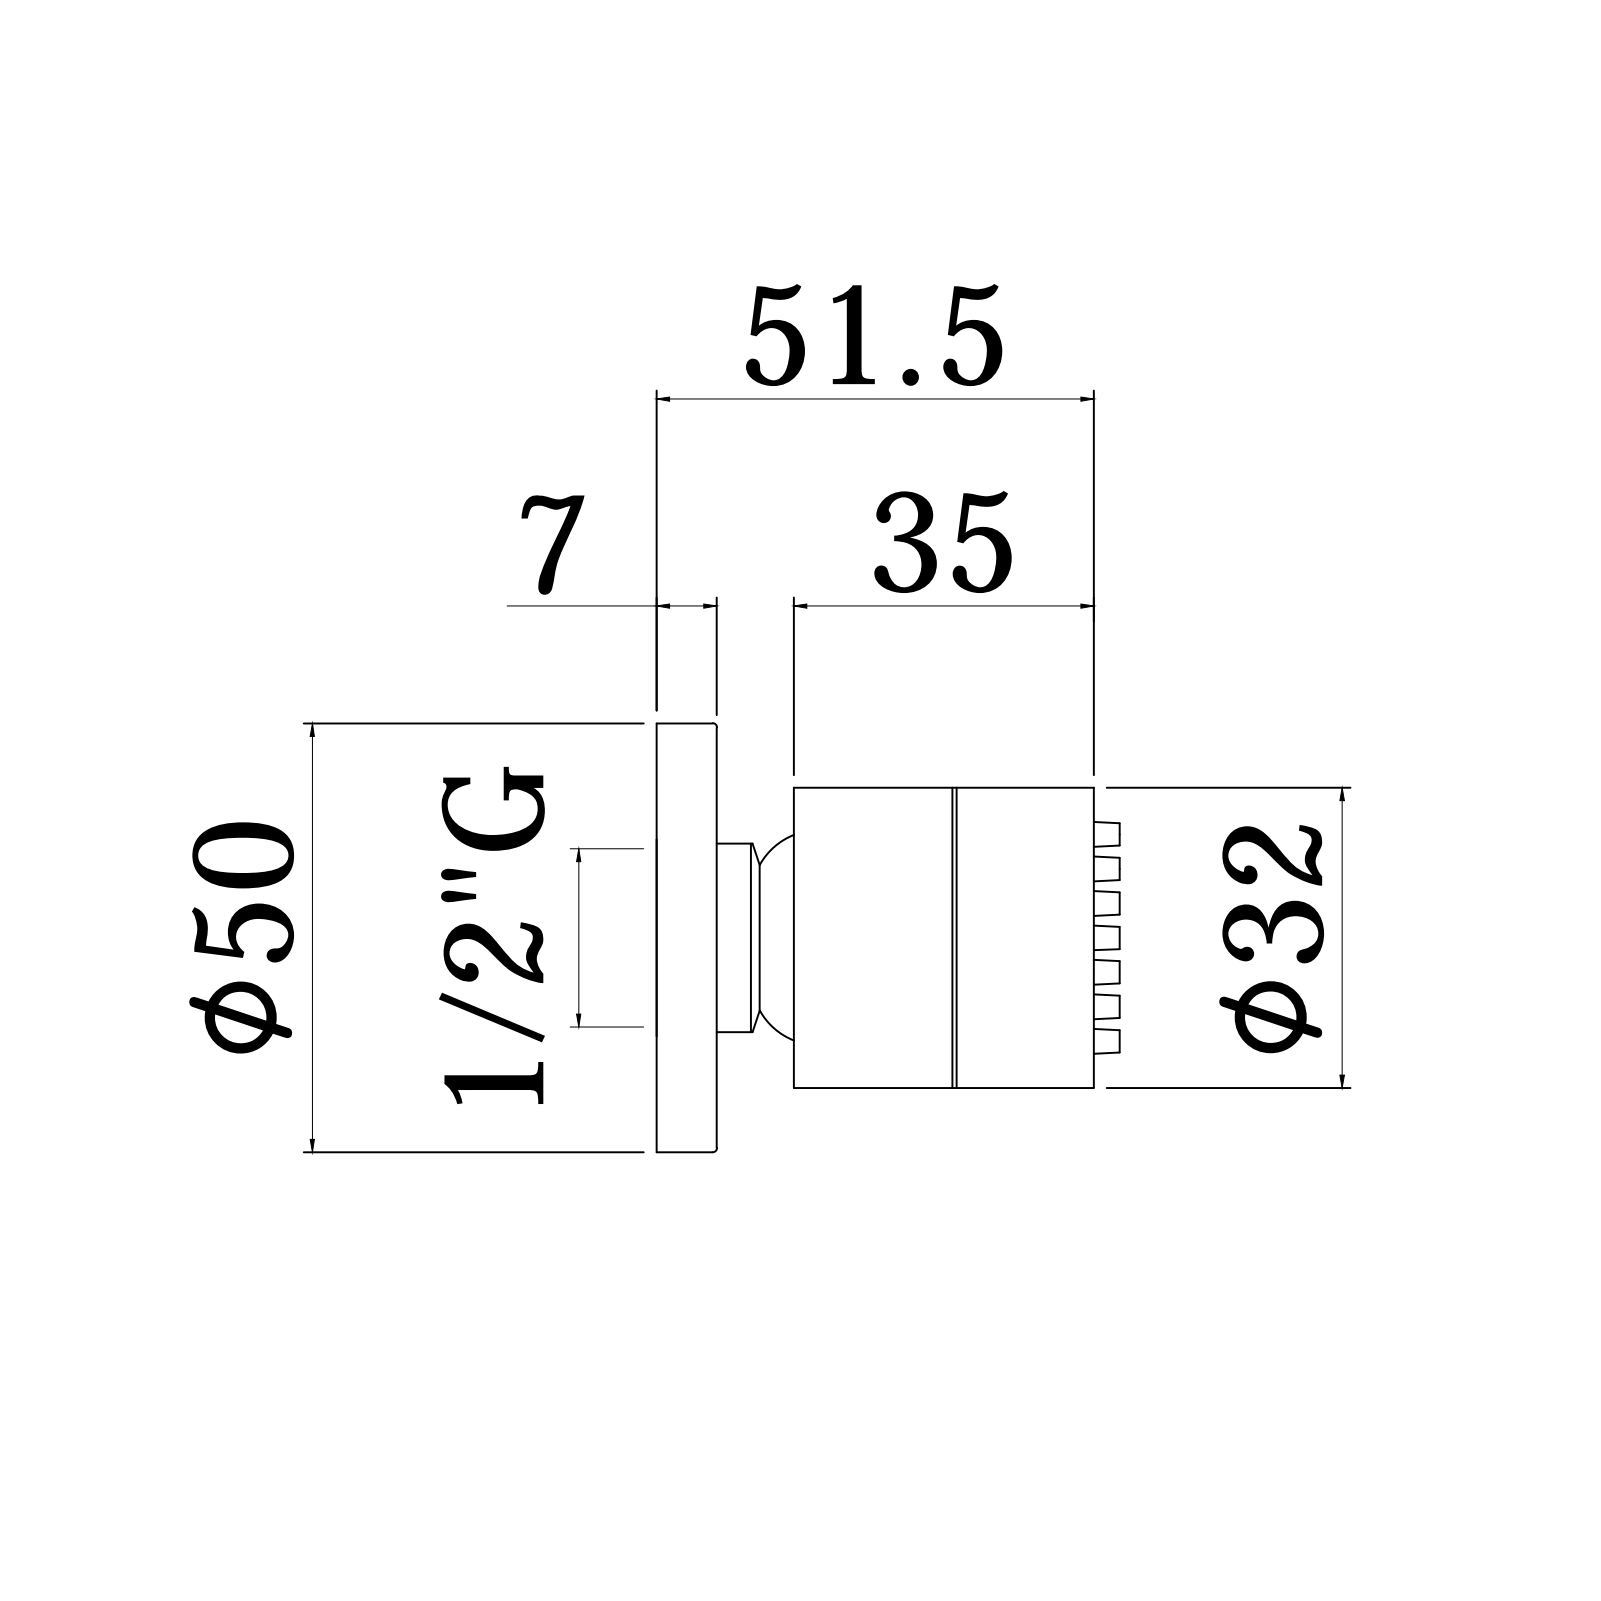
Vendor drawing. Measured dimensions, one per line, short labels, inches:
name: ZSOF061CR
written by: CREO PARAMETRIC BY PTC INC, 2020044 (CONFIG_CONTROL_DESIGN)
unit: in
bodies: 2 solids, 325 faces (59 planar, 116 cylindrical, 150 other)
size: 2.114 × 1.969 × 1.969
volume: 1.321 in³; area: 30.69 in²
holes: 13× ⌀0.118, 1× ⌀0.268, 1× ⌀0.591, 1× ⌀0.65, 1× ⌀0.74, 1× ⌀0.827, 1× ⌀0.906, 1× ⌀0.945, 1× ⌀0.961, 1× ⌀1, 1× ⌀1.047, 1× ⌀1.102
bosses: 1× ⌀1.26, 1× ⌀1.063, 1× ⌀0.866, 1× ⌀0.717
rounds: 2× R0.016
face distances: 1.858, 0.677, 0.157, 1.701, 0.177, 0.787, 1.358, 1.201, 0.5, 2.035
hole spacings: 0.158, 0.223, 0.273, 0.291, 0.381, 0.412, 0.441, 0.539
